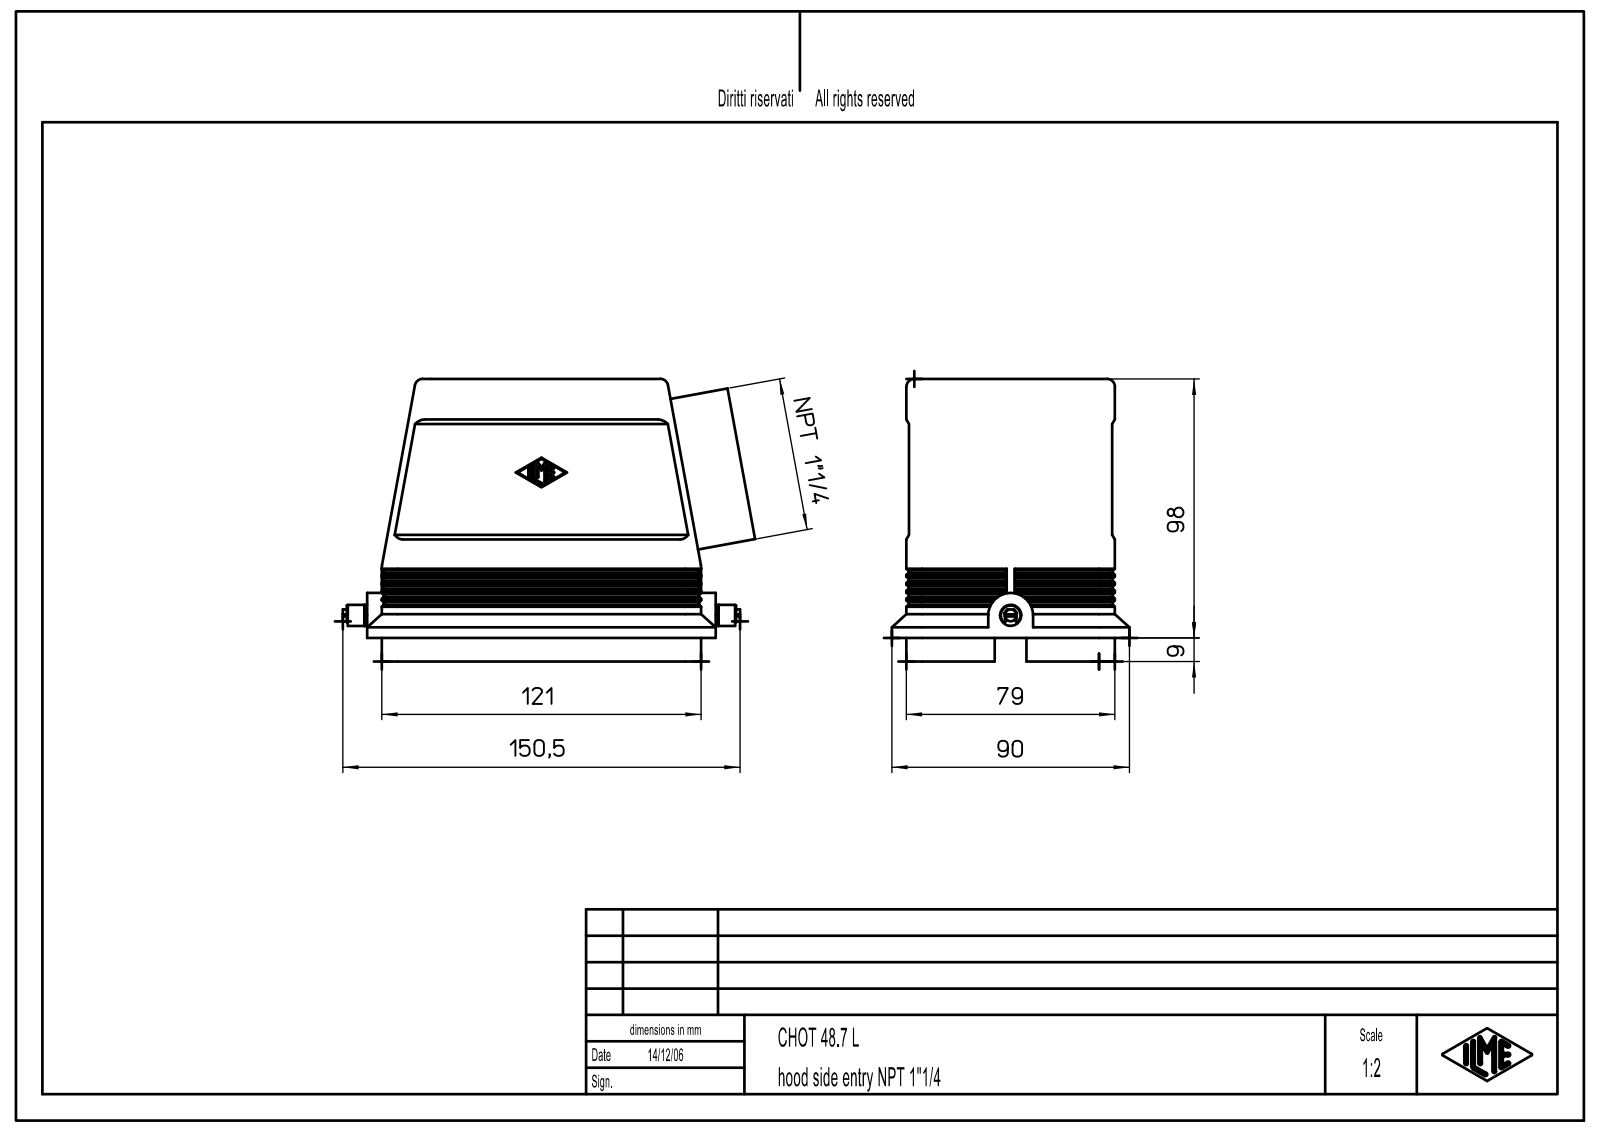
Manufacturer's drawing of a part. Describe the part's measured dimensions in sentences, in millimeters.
The part is named "MSBO11589". Its 3-D file was written by "Creo Elements/Direct Modeling 18.0B 02-Dec-2011 (C) Parametric Technology GmbH (AUTOMOTIVE_DESIGN)". It is 1 solid with 586 faces: 313 planar, 187 cylindrical and 86 other. Overall it measures 150.5 by 107 by 90 millimeters. Its volume is 239 465 cubic millimeters and its surface area 101 022 square millimeters. Round holes: 8 of diameter 3.5, 5 of diameter 2.46, 3 of diameter 2.46, 1 of diameter 6, 1 of diameter 48. Round bosses or shafts: 1 of diameter 46, 1 of diameter 43, 1 of diameter 40, 1 of diameter 8, 1 of diameter 4.5, 1 of diameter 3.5. Partial cylindrical surfaces (rounded edges, fillets, slot ends): 14 of radius 0.38, 12 of radius 2, 10 of radius 6, 4 of radius 0.5, 4 of radius 3, 4 of radius 5, 4 of radius 11.5, 3 of radius 0.95. The main face-to-face distances are 2.5, 74.5, 72, 3.5, 1, 75.5, 78, 13, 77, 8.5. The hole center spacings are 27, 35, 104, 107.45, 109.73, 8, 62, 104.31.
